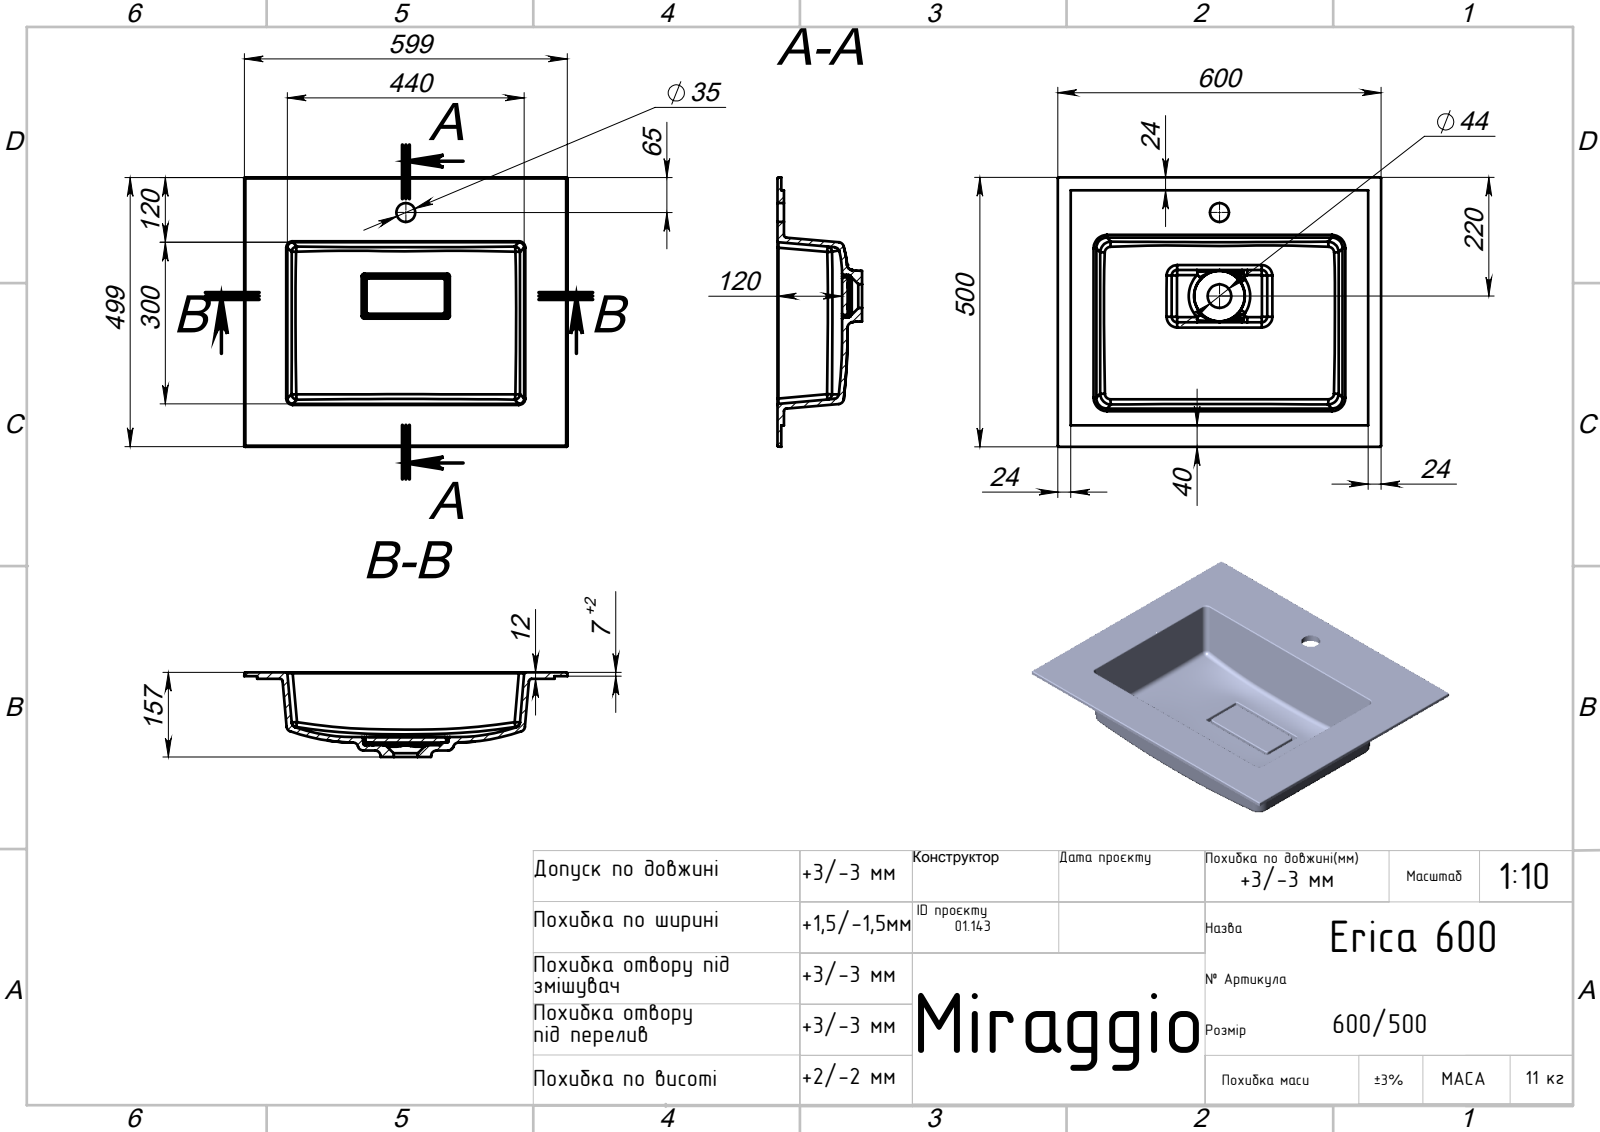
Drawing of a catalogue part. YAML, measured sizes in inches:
part_name: "Erica 600"
step_written_by: "SolidWorks 2020 (AUTOMOTIVE_DESIGN)"
units: inches
bodies: {solids: 2, faces: 244, planar: 44, cylindrical: 69, other: 131}
overall_size: [23.622, 19.685, 6.181]
volume: 284.6
surface_area: 1436
round_holes:
  - {diameter: 1.378, count: 1}
partial_cylinders:
  - {radius: 0.079, count: 26}
  - {radius: 0.118, count: 18}
  - {radius: 0.236, count: 6}
  - {radius: 0.197, count: 4}
  - {radius: 0.394, count: 4}
  - {radius: 0.787, count: 4}
face_to_face_distances: [0.472, 0.394, 0.197, 0.276, 0.393, 4.843, 4.646, 5.118, 4.252, 4.449]
